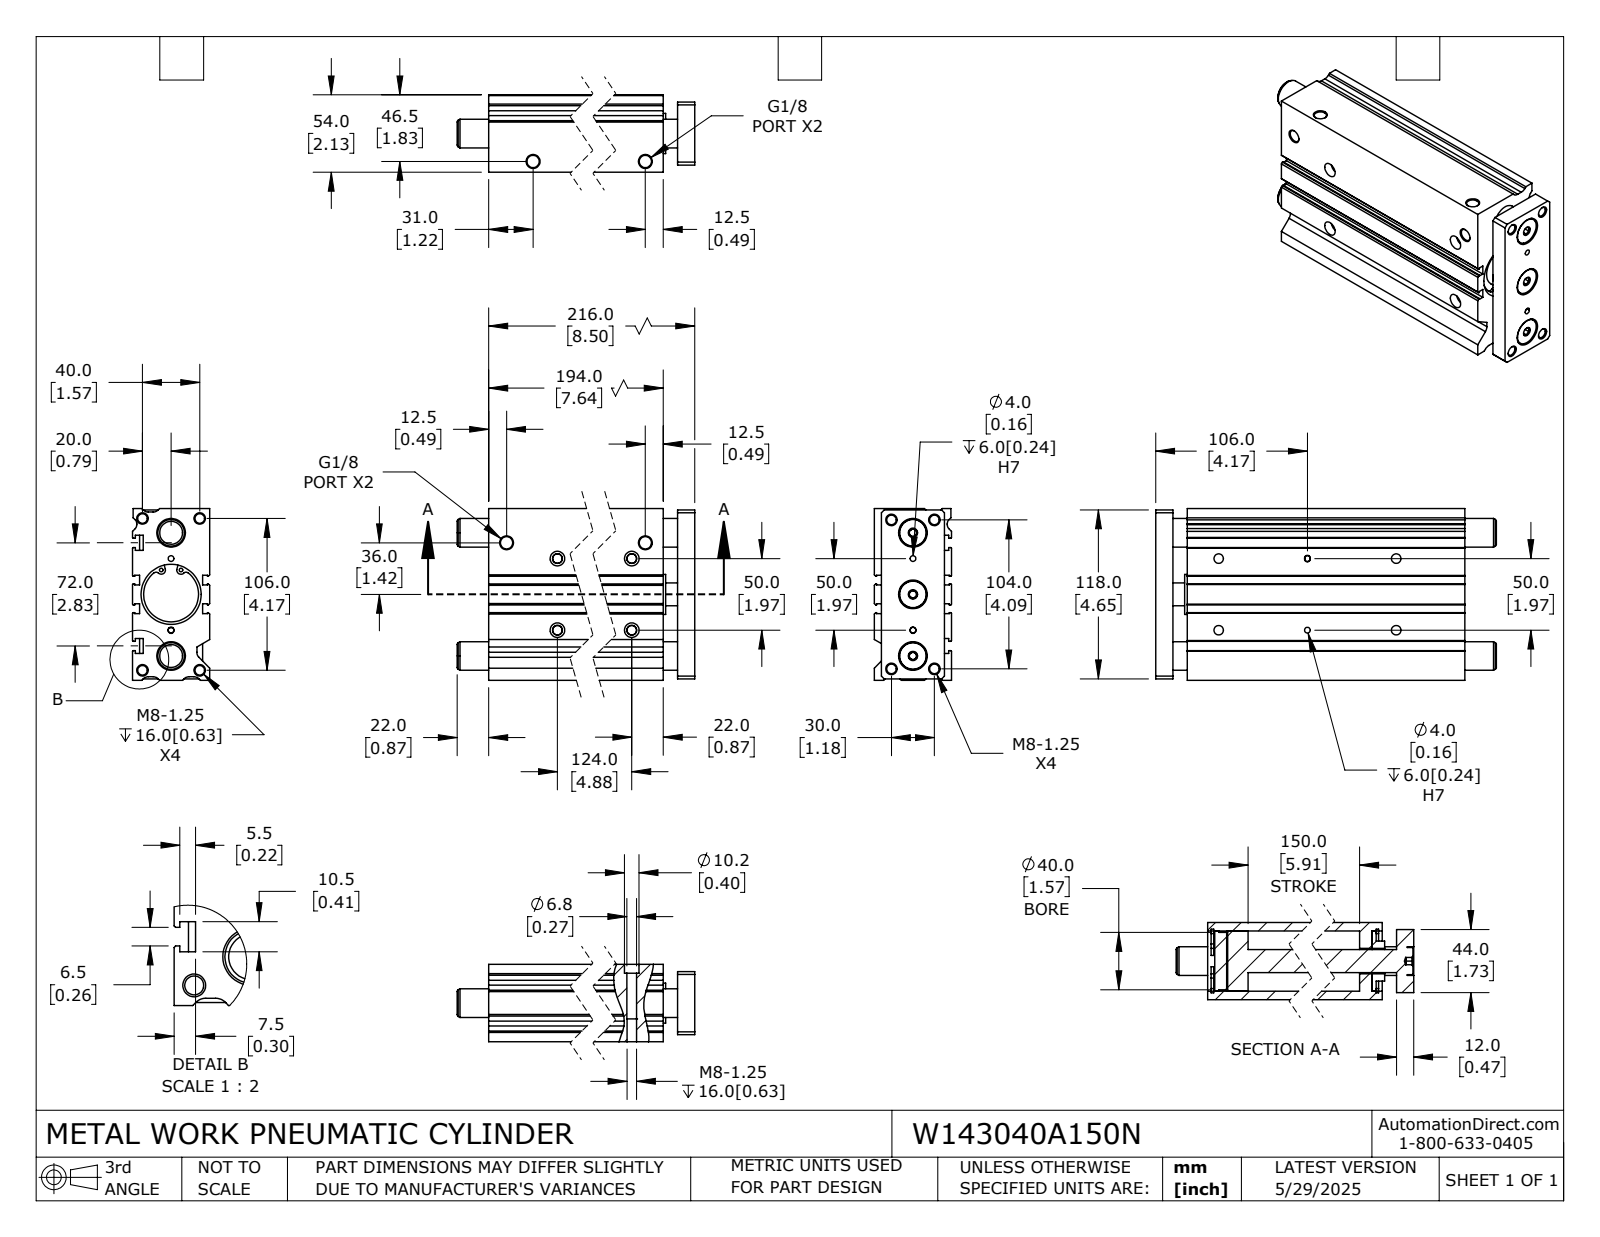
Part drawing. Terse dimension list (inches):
name: W143040A150N_BODY; W143040A150N; W143040A150N_ROD
written by: SolidWorks 2024 (CONFIG_CONTROL_DESIGN)
unit: in
bodies: 6 solids, 393 faces (192 planar, 151 cylindrical, 50 other)
size: 9.37 × 4.724 × 2.126
volume: 63.79 in³; area: 346.3 in²
holes: 12× ⌀0.262, 4× ⌀0.098, 4× ⌀0.157, 4× ⌀0.268, 4× ⌀0.337, 4× ⌀0.402, 3× ⌀0.197, 3× ⌀0.787, 1× ⌀0.697, 1× ⌀1.51
bosses: 3× ⌀0.748, 2× ⌀1.752, 1× ⌀1.654, 1× ⌀1.575, 1× ⌀1.102, 1× ⌀0.63
rounds: 7× R0.197, 4× R0.079, 4× R0.089, 4× R0.116, 2× R0.157
face distances: 2.126, 0.197, 1.929, 0.098, 4.724, 0.866, 0.295, 1.831, 8.504, 1.634
hole spacings: 0.201, 0.415, 0.689, 0.722, 0.88, 1.059, 1.216, 1.355
